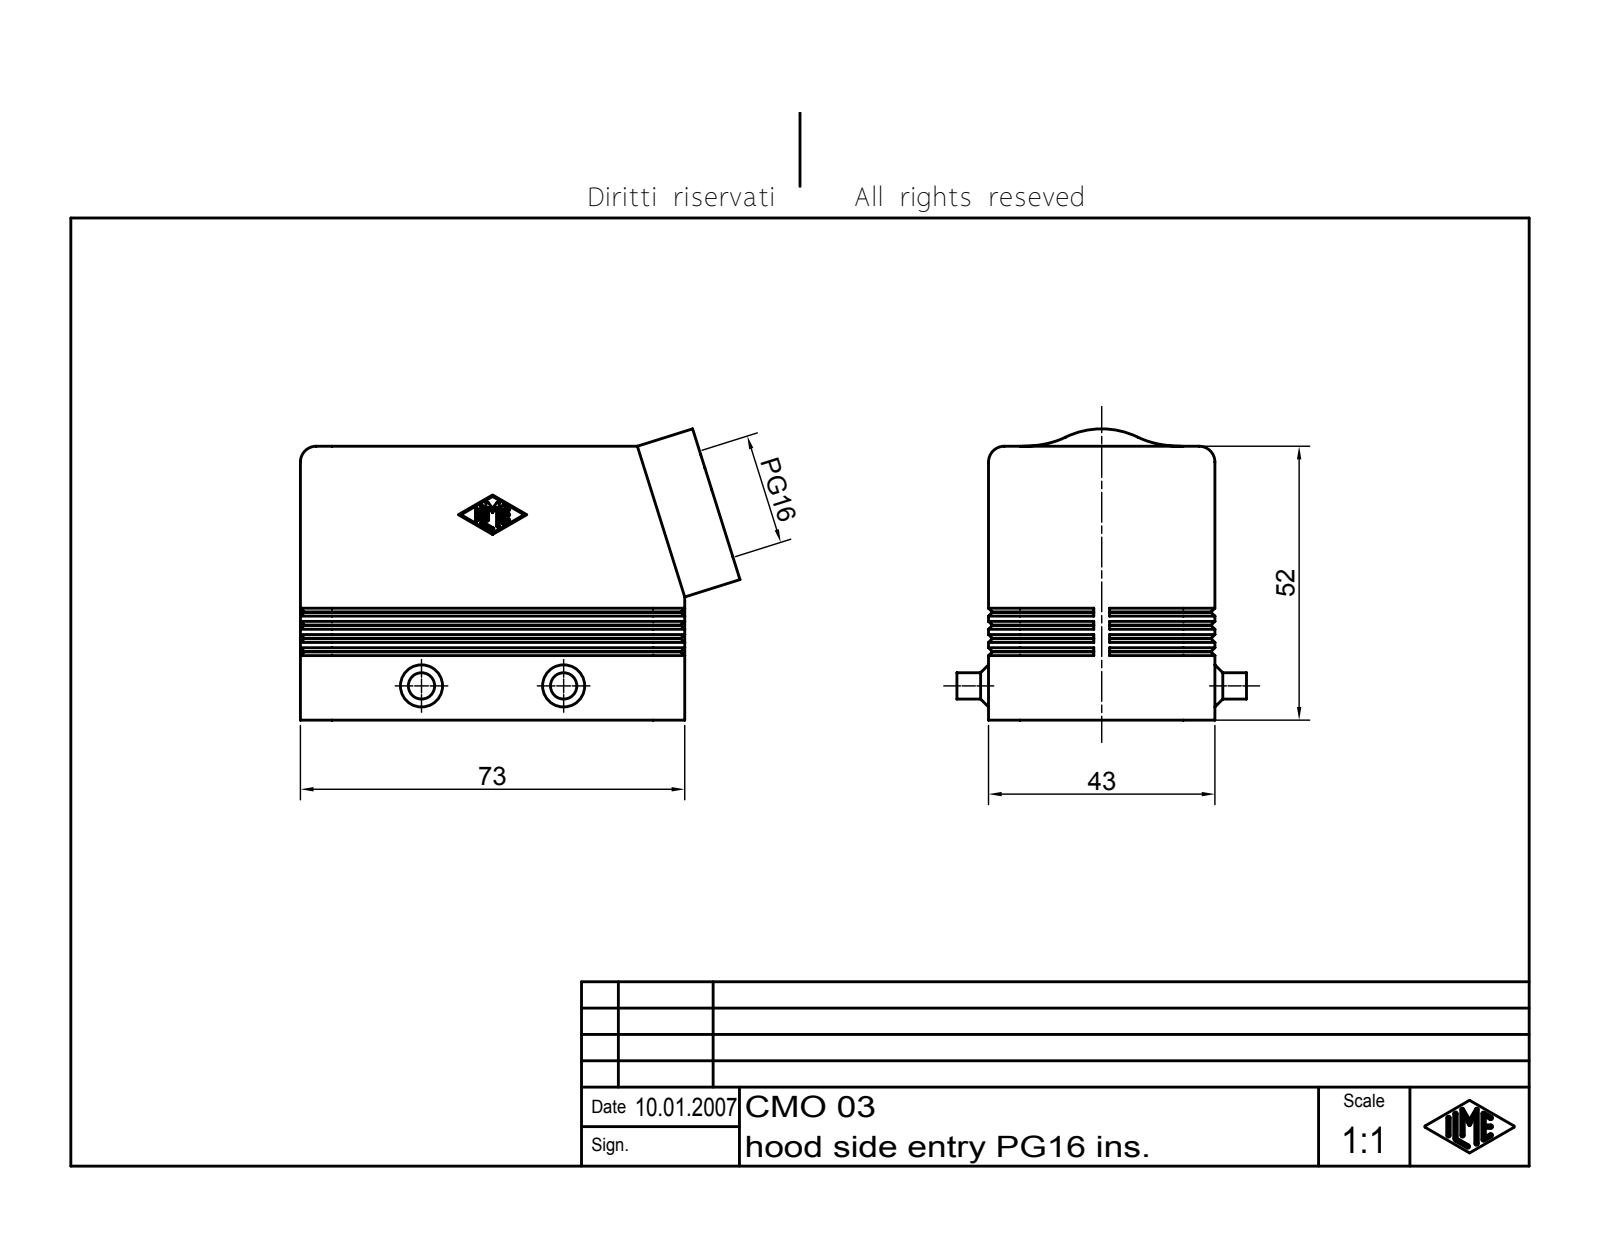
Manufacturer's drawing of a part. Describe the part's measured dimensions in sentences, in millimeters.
The part is named "CHO Tüllengehäuse 2 Bügel für einen Einsatz". Its 3-D file was written by "Autodesk Inventor 7 (AUTOMOTIVE_DESIGN)". It is 1 solid with 388 faces: 145 planar, 89 cylindrical and 154 other. Overall it measures 83.49 by 55.3 by 55 millimeters. Its volume is 54 634 cubic millimeters and its surface area 29 410 square millimeters. Round holes: 1 of diameter 19.16, 1 of diameter 21.16. Round bosses or shafts: 2 of diameter 5. Partial cylindrical surfaces (rounded edges, fillets, slot ends): 14 of radius 0.25, 7 of radius 3, 4 of radius 2, 4 of radius 6, 2 of radius 5.3, 1 of radius 1.5. The main face-to-face distances are 3, 40, 43, 37, 11.5, 8.5, 70, 61.5, 58.5, 20.
